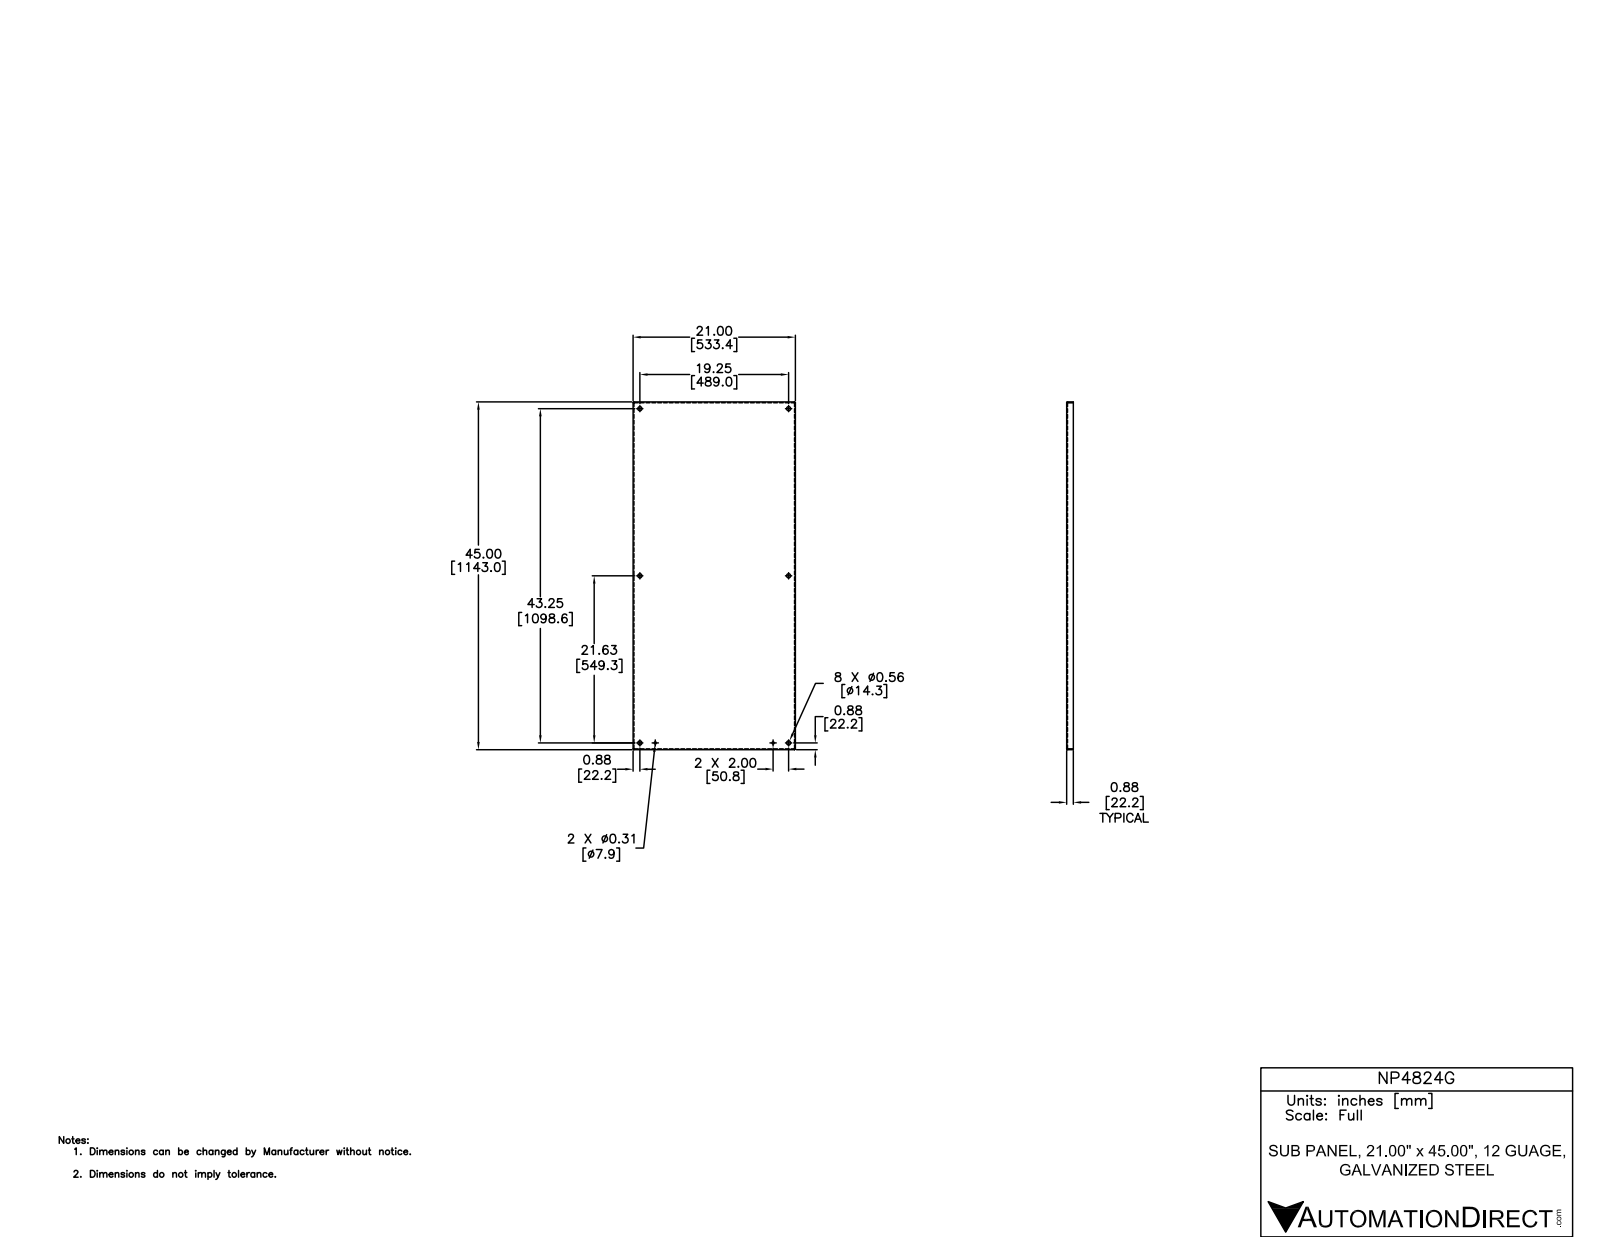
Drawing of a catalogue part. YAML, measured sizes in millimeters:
part_name: "NP4824G"
step_written_by: "Autodesk Inventor 2012 (AUTOMOTIVE_DESIGN)"
units: millimeters
bodies: {solids: 1, faces: 46, planar: 22, cylindrical: 16, other: 8}
overall_size: [1143, 533.4, 22.2]
volume: 1599000
surface_area: 1353000
round_holes:
  - {diameter: 14.3, count: 6}
  - {diameter: 7.9, count: 2}
partial_cylinders:
  - {radius: 0.8, count: 4}
  - {radius: 3.2, count: 4}
face_to_face_distances: [2.4, 531, 533.4, 528.7, 1140.6, 1143, 1138.3, 19.8, 22.2, 2.7]
hole_center_spacings: [549.3, 735.4, 489, 702.6, 1098.6, 1099.7, 1202.5, 50.8]
